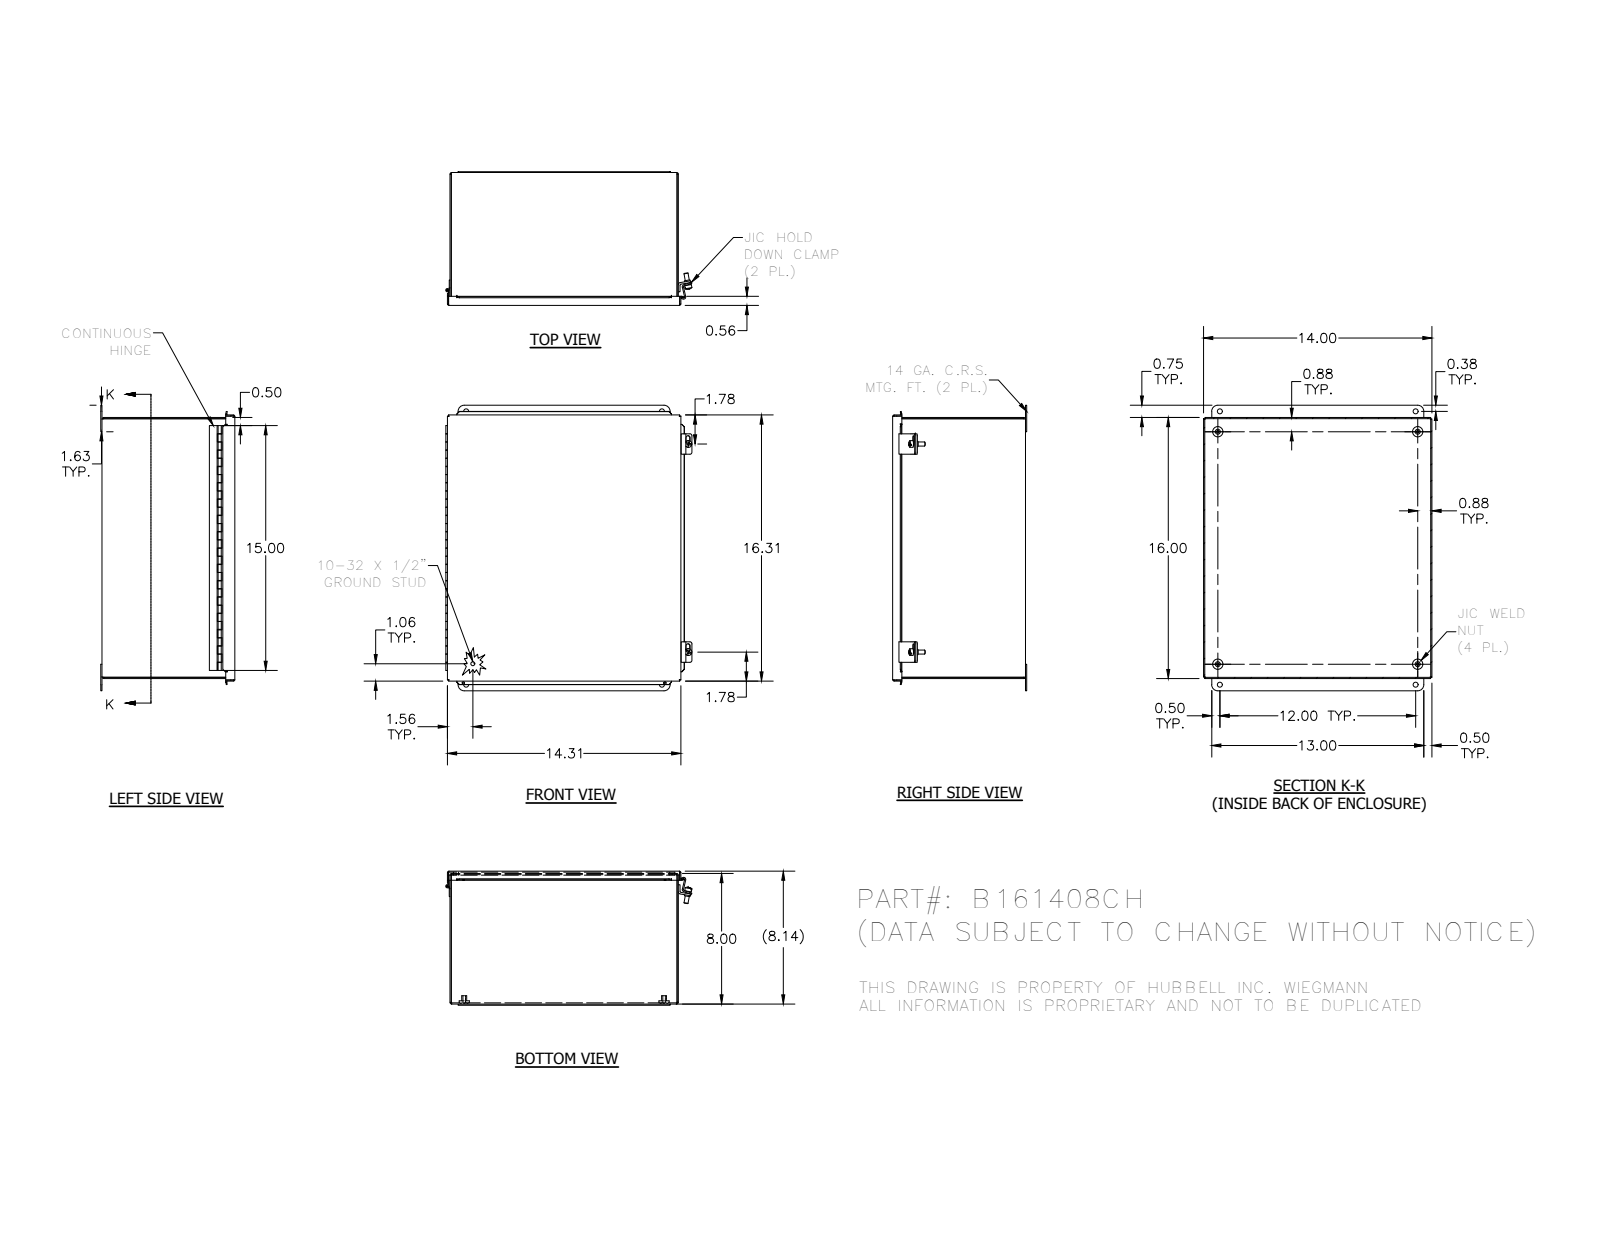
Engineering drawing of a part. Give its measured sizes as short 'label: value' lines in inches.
name: B161408CH; 3499; 3486; C1001 (+8 more)
written by: Autodesk Inventor 2012 (AUTOMOTIVE_DESIGN)
unit: in
bodies: 20 solids, 539 faces (347 planar, 147 cylindrical, 45 other)
size: 17.5 × 15.087 × 8.219
volume: 81.47 in³; area: 2 244 in²
holes: 4× ⌀0.156, 4× ⌀0.31, 2× ⌀0.14, 2× ⌀0.196, 1× ⌀0.116
bosses: 4× ⌀0.625, 4× ⌀0.3, 3× ⌀0.25, 2× ⌀0.41, 2× ⌀0.344, 1× ⌀0.2, 1× ⌀0.19, 1× ⌀0.1
rounds: 15× R0.031, 8× R0.105, 8× R0.125, 7× R0.093, 4× R0.133, 4× R0.375, 3× R0.063, 3× R0.126
face distances: 0.074, 8.083, 13.926, 0.062, 8.144, 8.009, 8.07, 15.926, 14, 13.852
hole spacings: 1.256, 12.189, 15.501, 19.68, 12, 12.25, 14.25, 16.75
